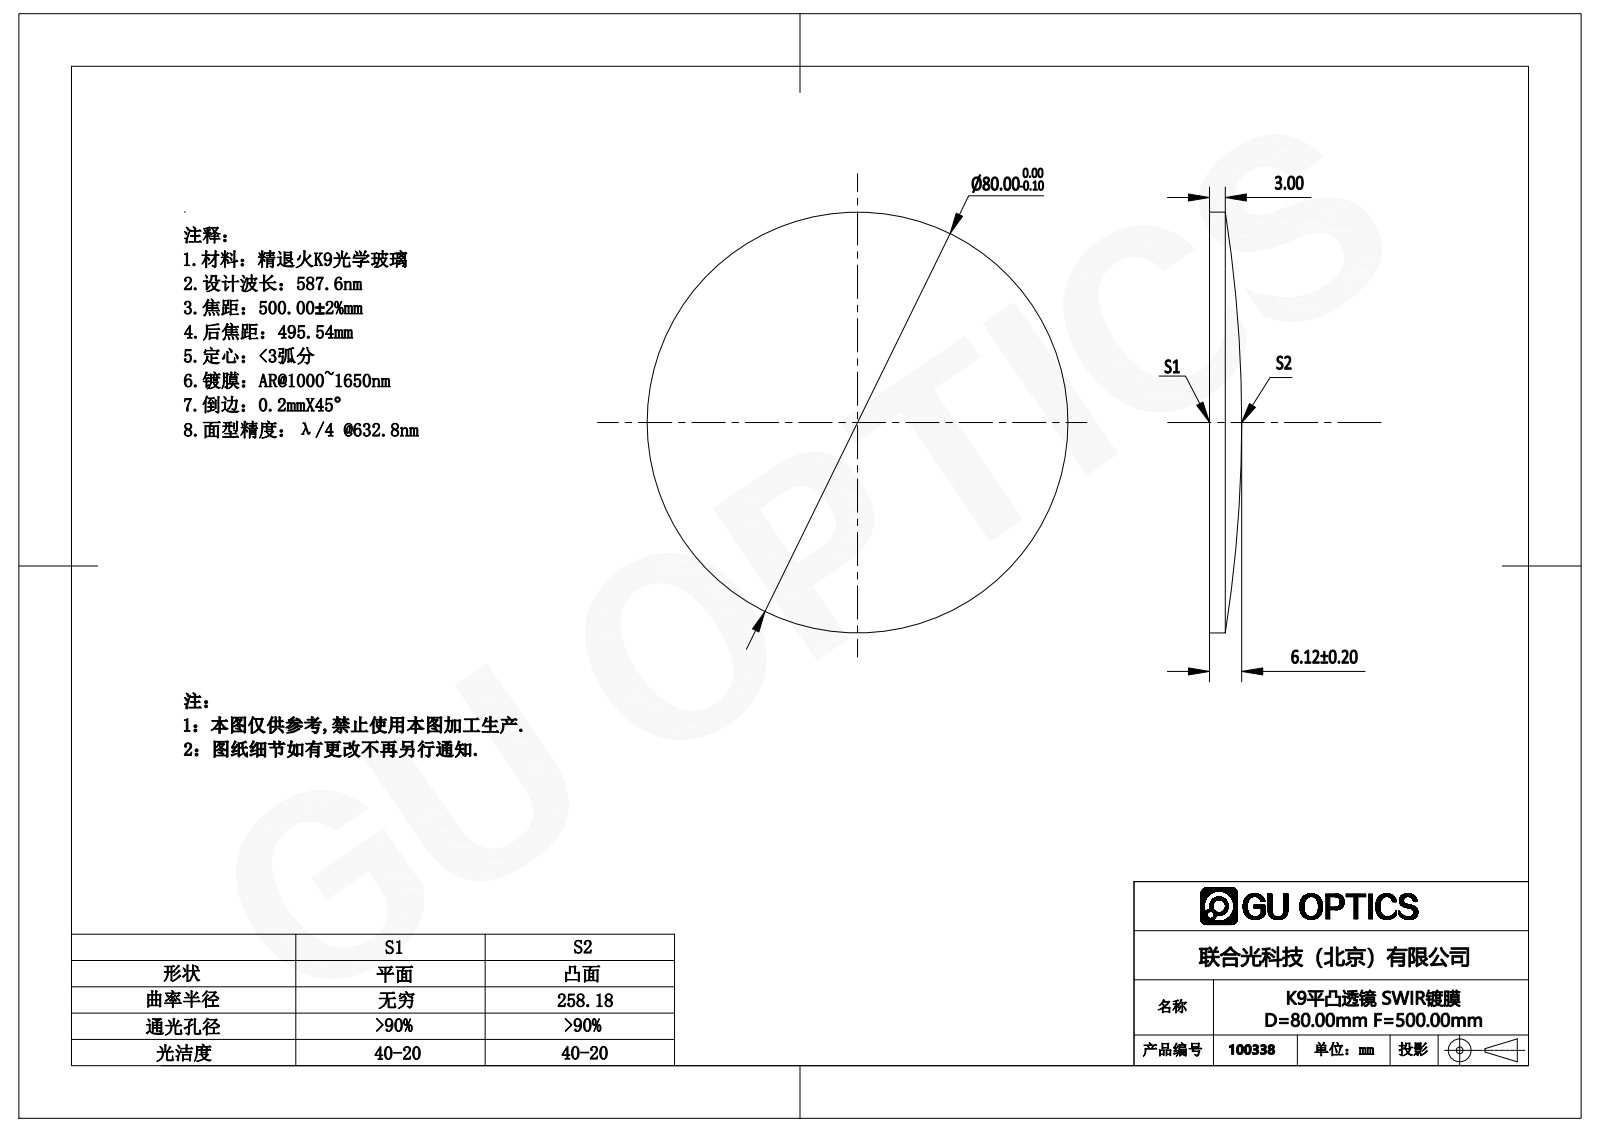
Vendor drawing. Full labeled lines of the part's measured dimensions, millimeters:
Part name (STEP PRODUCT): 100166
STEP written by: SolidWorks 2016 (AUTOMOTIVE_DESIGN)
Units: millimetres
Bodies: 1 solid, 5 faces (1 planar, 2 cylindrical, 2 other)
Overall size (bounding box): 80 × 80 × 6.12
Volume: 22 937 mm³ · Surface area: 10 838 mm²
Round bosses / shafts (diameter × count): ⌀80 ×1
